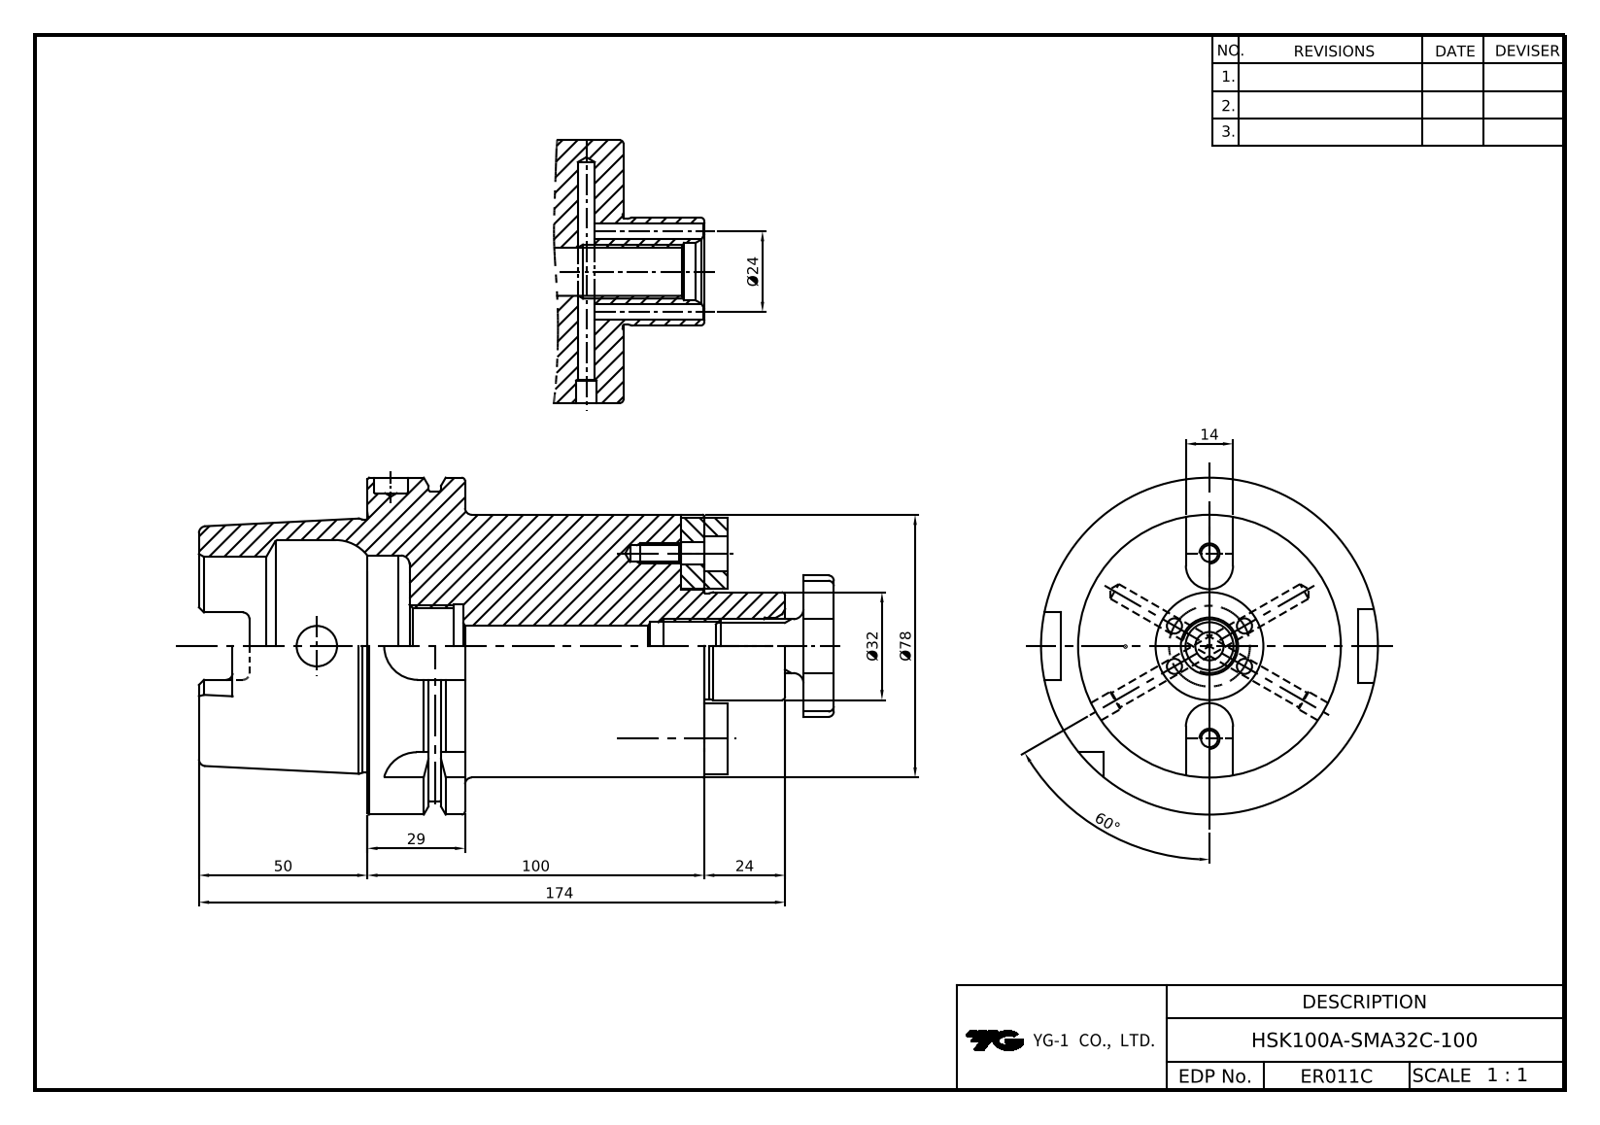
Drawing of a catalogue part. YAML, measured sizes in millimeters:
part_name: "LO-HSK100A-SMA32C-100; SMA32E-DRIVE KEY-SECO; HEX'' WRENCH BOLT-M6x1.0x15L; SMA32-M16x2.0x26L"
step_written_by: "Autodesk Inventor 2025 (AP242_MANAGED_MODEL_BASED_3D_ENGINEERING_MIM_LF)"
units: millimeters
bodies: {solids: 6, faces: 207, planar: 85, cylindrical: 62, other: 60}
overall_size: [193, 100, 100]
volume: 617052
surface_area: 85456
round_holes:
  - {diameter: 4.5, count: 4}
  - {diameter: 4.92, count: 2}
  - {diameter: 6.6, count: 2}
  - {diameter: 10, count: 2}
  - {diameter: 10.5, count: 2}
  - {diameter: 12, count: 1}
  - {diameter: 13.84, count: 1}
  - {diameter: 17, count: 1}
  - {diameter: 22.38, count: 1}
  - {diameter: 25, count: 1}
  - {diameter: 53, count: 1}
  - {diameter: 63, count: 1}
round_bosses_or_shafts:
  - {diameter: 10, count: 2}
  - {diameter: 6, count: 2}
  - {diameter: 100, count: 1}
  - {diameter: 92, count: 1}
  - {diameter: 78, count: 1}
  - {diameter: 75.41, count: 1}
  - {diameter: 32, count: 1}
  - {diameter: 16, count: 1}
partial_cylinders:
  - {radius: 2, count: 6}
  - {radius: 3, count: 4}
  - {radius: 4.88, count: 4}
  - {radius: 7, count: 4}
  - {radius: 10, count: 4}
  - {radius: 21, count: 1}
face_to_face_distances: [100, 29, 71, 143, 50, 12.5, 16.5, 87.5, 7, 64]
hole_center_spacings: [12, 23.88, 35.07, 20.78, 24, 27.5, 55]
